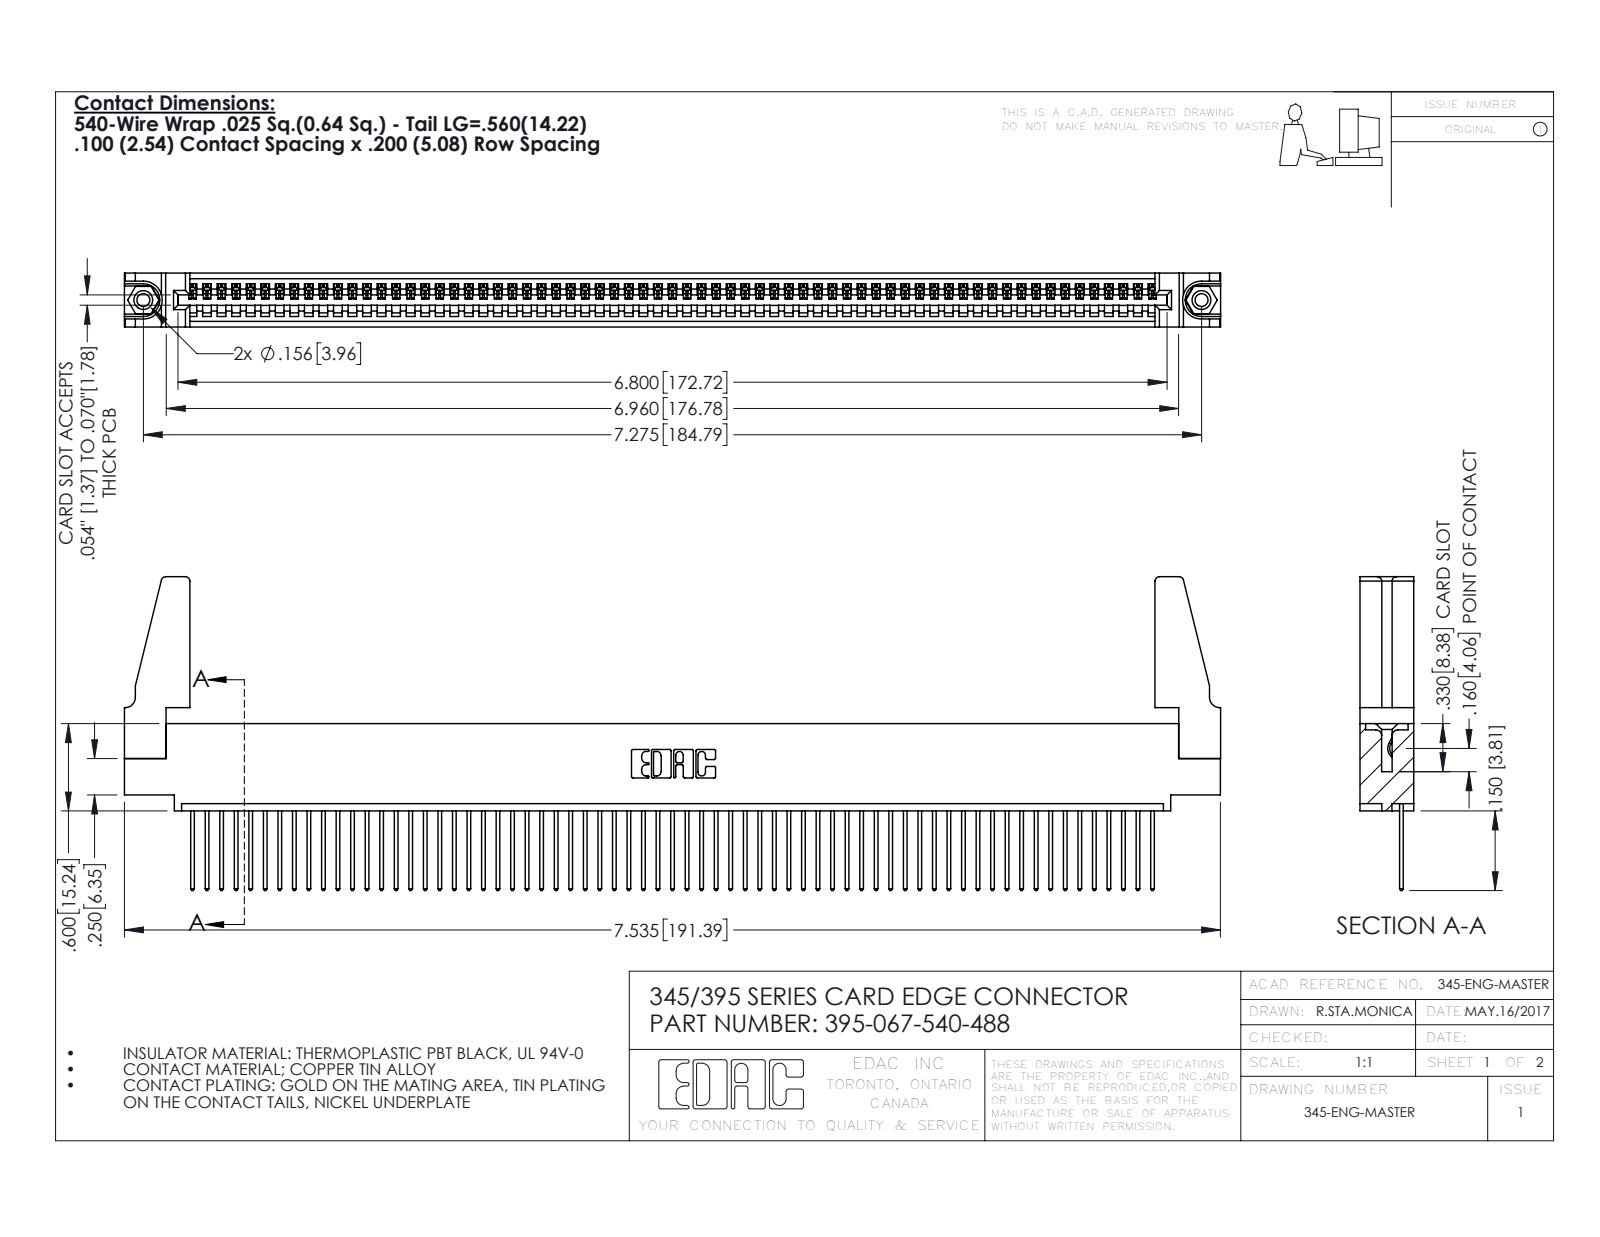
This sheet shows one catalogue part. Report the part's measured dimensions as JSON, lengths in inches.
{"part_name": "395-067-540-488; 345-292-001_345-293-140; 345 Part_0.110 Offset - 0.156 Dia-TH; 345-250-001_345-250-001-102 (+1 more)", "step_written_by": "SolidWorks 2016 (CONFIG_CONTROL_DESIGN)", "units": "inches", "bodies": {"solids": 72, "faces": 4140, "planar": 2836, "cylindrical": 1288, "other": 16}, "overall_size": [7.536, 2.157, 0.37], "volume_in3": 1.321, "surface_area_in2": 44.42, "round_holes": [[0.089, 2], [0.125, 2], [0.156, 2], [0.064, 1]], "round_bosses_or_shafts": [[0.155, 2]], "partial_cylinders_radius": [[0.006, 134], [0.01, 134], [0.01, 22], [0.03, 8], [0.007, 6], [0.031, 6], [0.026, 3], [0.031, 2]], "face_to_face_distances": [0.072, 0.298, 0.37, 0.098, 0.272, 0.025, 0.2, 0.225, 0.149, 0.072], "hole_center_spacings": [0.27, 7.039, 7.275]}
